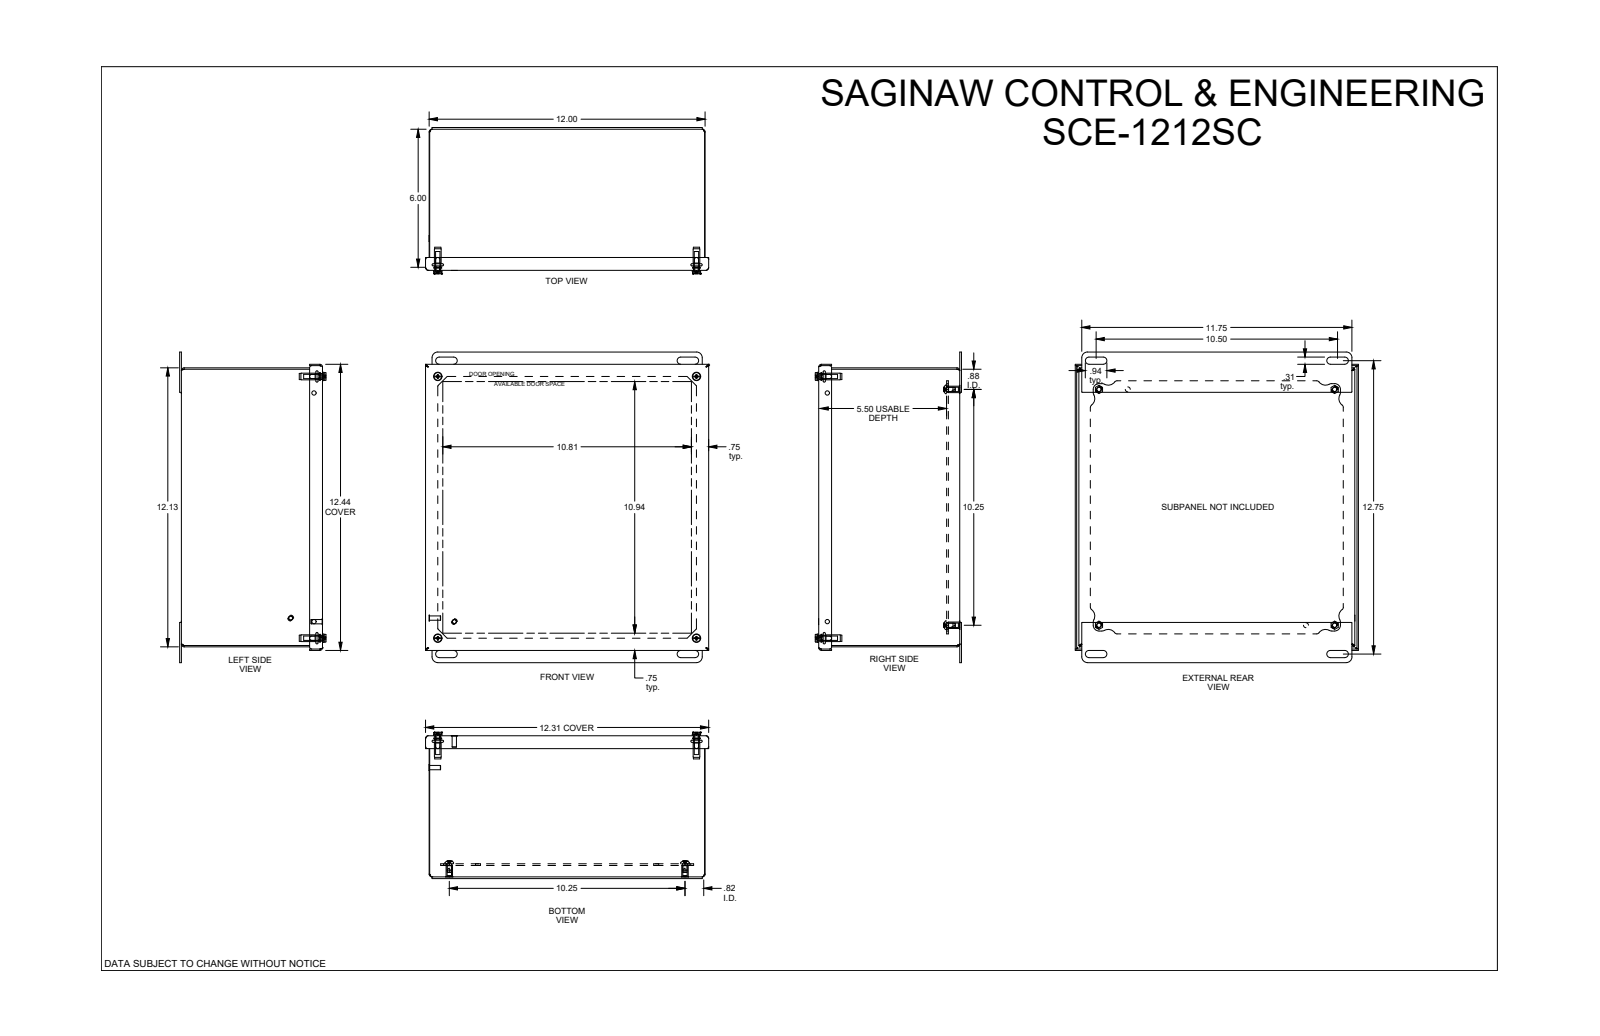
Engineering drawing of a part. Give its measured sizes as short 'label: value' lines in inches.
name: SCE-1212SC
written by: SolidWorks 2019 (AUTOMOTIVE_DESIGN)
unit: in
bodies: 28 solids, 805 faces (328 planar, 207 cylindrical, 270 other)
size: 13.5 × 12.313 × 6.361
volume: 50.77 in³; area: 1 623 in²
holes: 8× ⌀0.19, 8× ⌀0.25, 4× ⌀0.22, 4× ⌀0.266, 4× ⌀0.281, 4× ⌀0.317, 2× ⌀0.187, 2× ⌀0.218, 1× ⌀0.193
bosses: 10× ⌀0.188, 4× ⌀0.437, 4× ⌀0.373, 4× ⌀0.362, 4× ⌀0.34, 4× ⌀0.334, 4× ⌀0.292, 4× ⌀0.28
rounds: 16× R0.125, 16× R0.25, 12× R0.06, 8× R0.005, 8× R0.05, 8× R0.063, 8× R0.156, 8× R0.255
face distances: 0.06, 6.075, 6.135, 6.015, 11.94, 12.065, 5.505, 0.075, 0.57, 0.51
hole spacings: 0.753, 10.824, 15.247, 10.25, 10.765, 11.25, 11.375, 11.375
